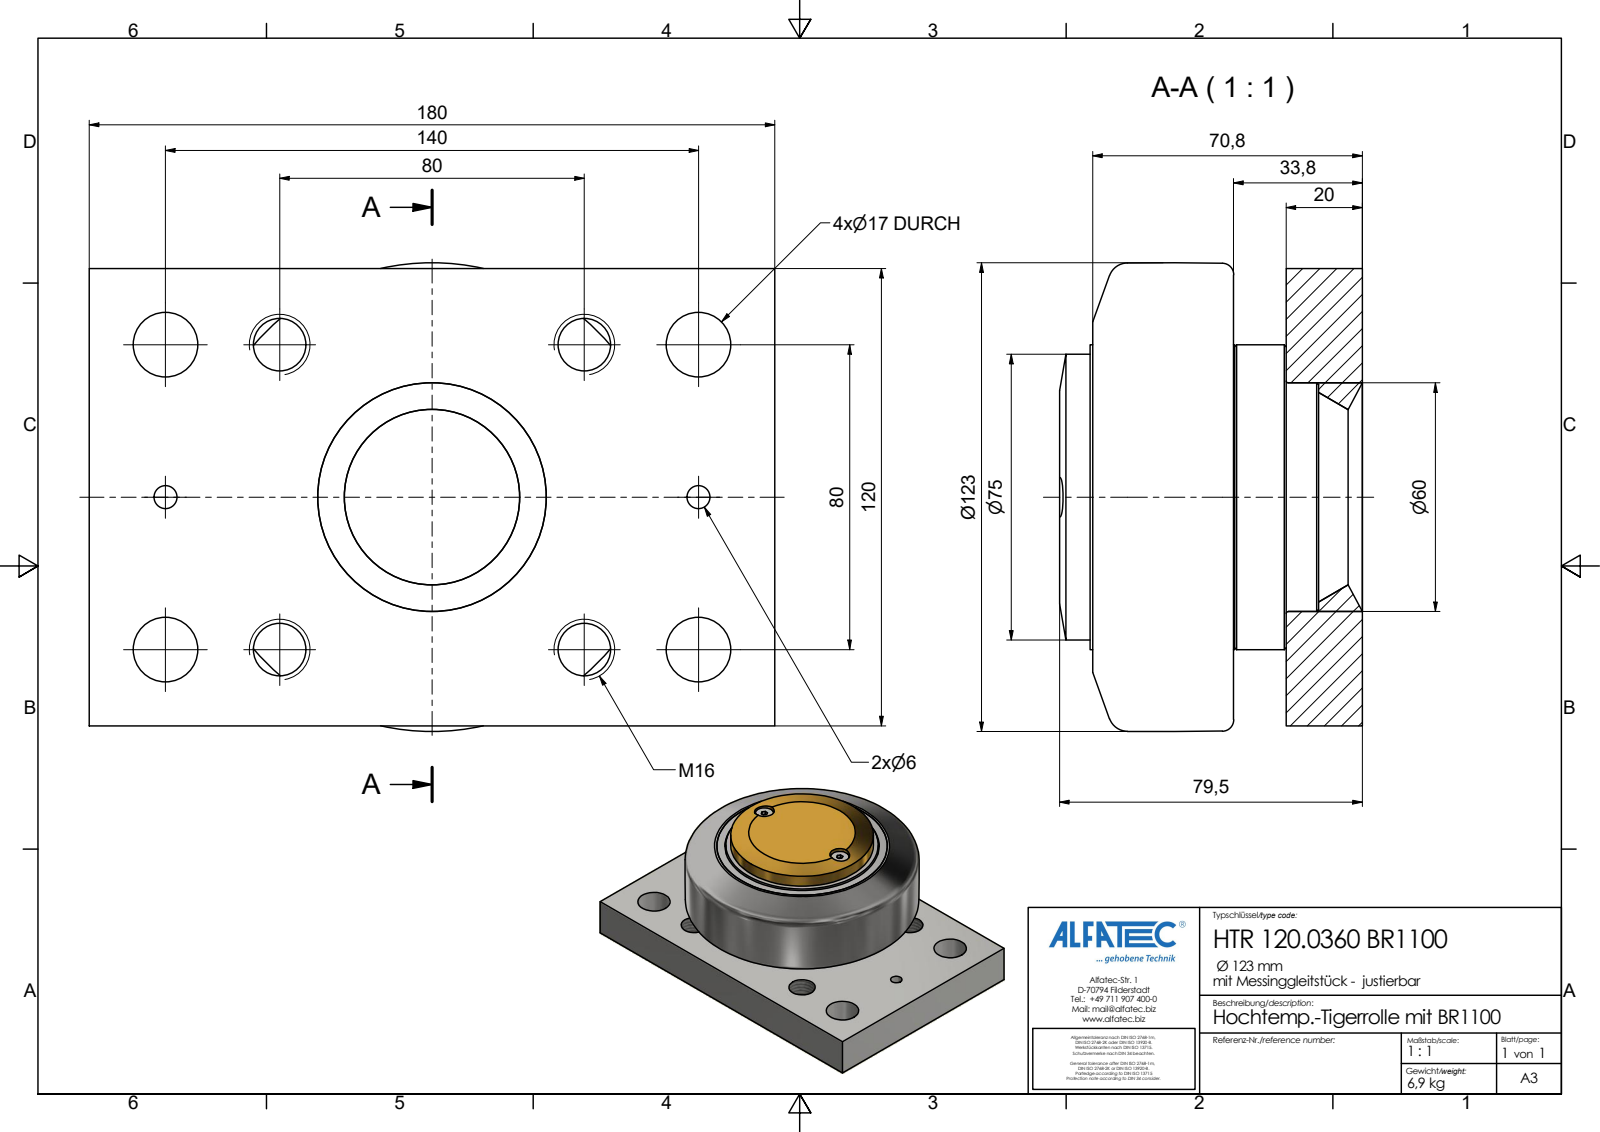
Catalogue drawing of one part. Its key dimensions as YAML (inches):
part_name: "HTR 120.0360 BR1100_Kontur"
step_written_by: "Autodesk Inventor 2020 (AP242_MANAGED_MODEL_BASED_3D_ENGINEERING_MIM_LF)"
units: inches
bodies: {solids: 1, faces: 54, planar: 27, cylindrical: 18, other: 9}
overall_size: [7.087, 4.843, 3.13]
volume: 56.69
surface_area: 141.9
round_holes:
  - {diameter: 0.545, count: 4}
  - {diameter: 0.669, count: 4}
  - {diameter: 0.236, count: 2}
  - {diameter: 0.409, count: 2}
round_bosses_or_shafts:
  - {diameter: 0.384, count: 2}
  - {diameter: 3.15, count: 1}
  - {diameter: 2.953, count: 1}
face_to_face_distances: [0.787, 1.331, 0.543, 4.724, 7.087, 3.13, 2.343, 1.799, 2.787, 2]
hole_center_spacings: [3.15, 1.181, 1.575, 1.644, 1.969, 2.283, 3.106, 3.364]
